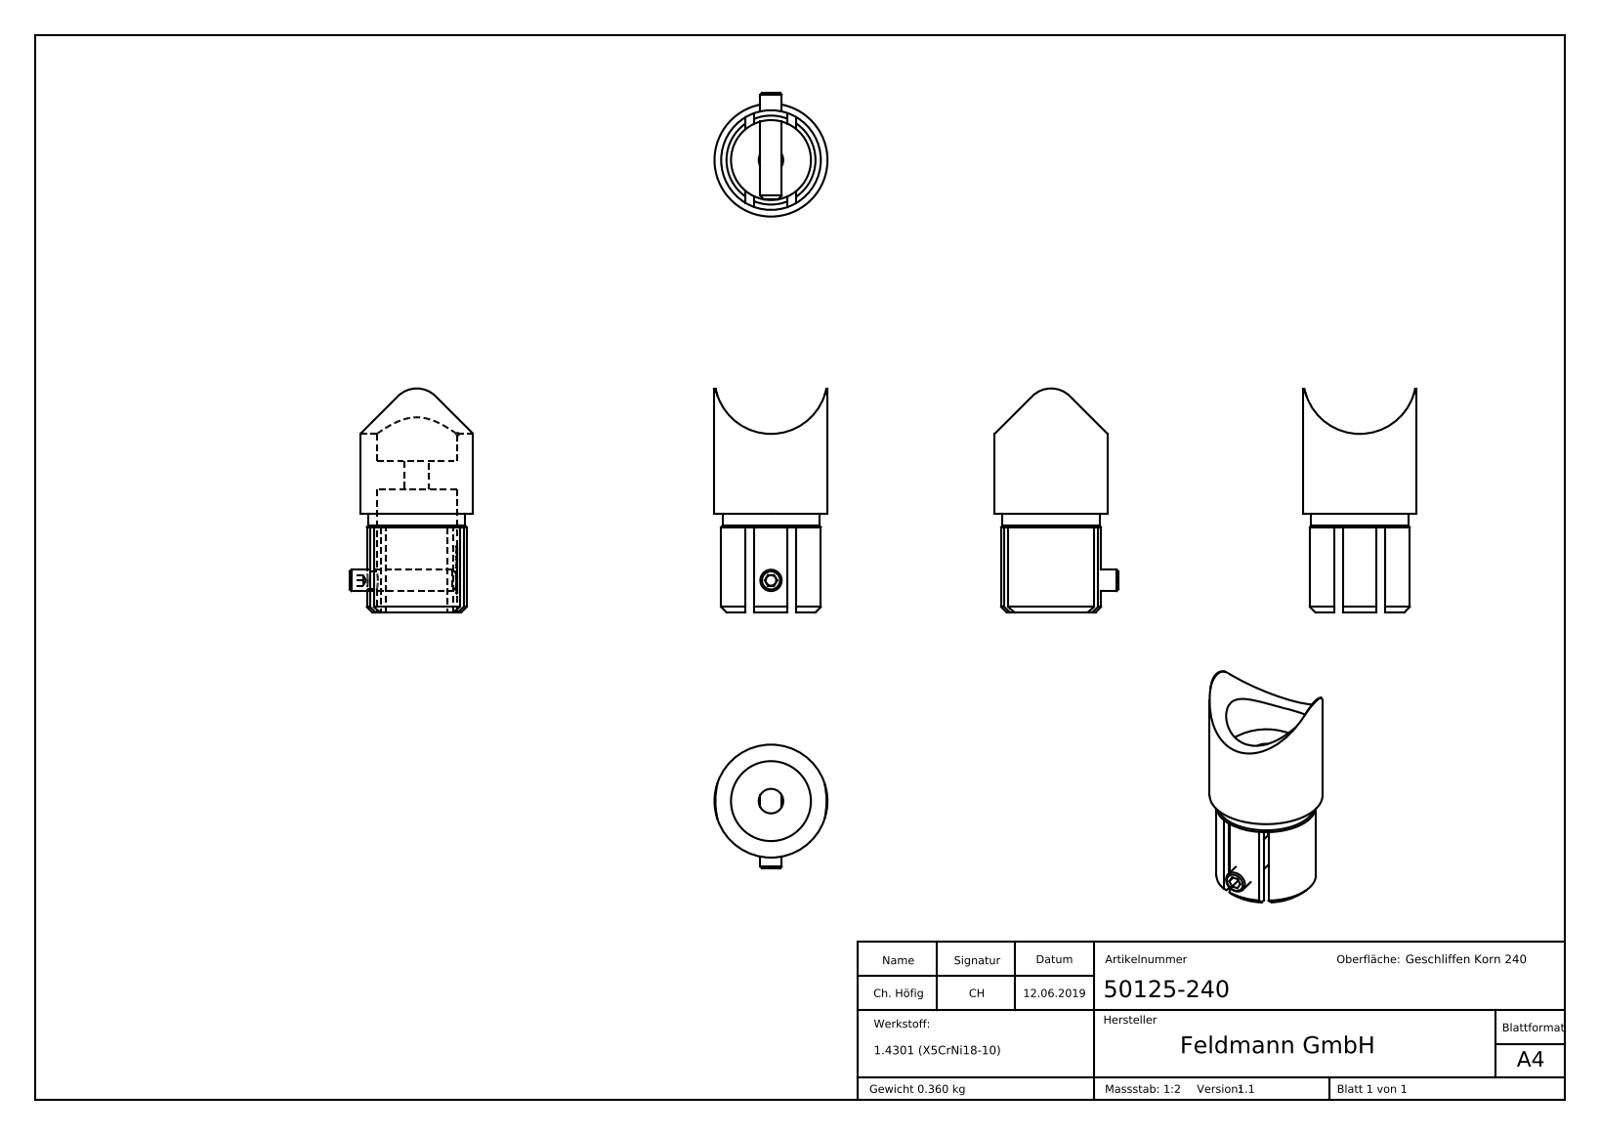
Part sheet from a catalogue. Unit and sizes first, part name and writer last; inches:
Units: inches
Overall size (bounding box): 3.309 × 1.827 × 1.669
Round holes (diameter × count): ⌀0.268 ×1, ⌀0.362 ×1, ⌀1.181 ×1
Round bosses / shafts (diameter × count): ⌀1.669 ×1, ⌀1.472 ×1, ⌀1.433 ×1, ⌀0.315 ×1
Partial cylindrical surfaces — rounded edges, fillets, slot ends (radius × count): R0.394 ×1, R0.594 ×1, R0.835 ×1
Main face-to-face distances: 0.421, 0.126, 0.622, 0.354, 0.776, 0.748, 0.496, 1.457, 1.811, 2.232
Volume: 2.782 in³ · Surface area: 30.13 in²
Bodies: 2 solids, 299 faces (134 planar, 58 cylindrical, 107 other)
Part name (STEP PRODUCT): DIN913_DIN 913 M8x40; 5012X-240 Teil1_50125-240 Teil1; 50125-240
STEP written by: SolidWorks 2015 (CONFIG_CONTROL_DESIGN)
